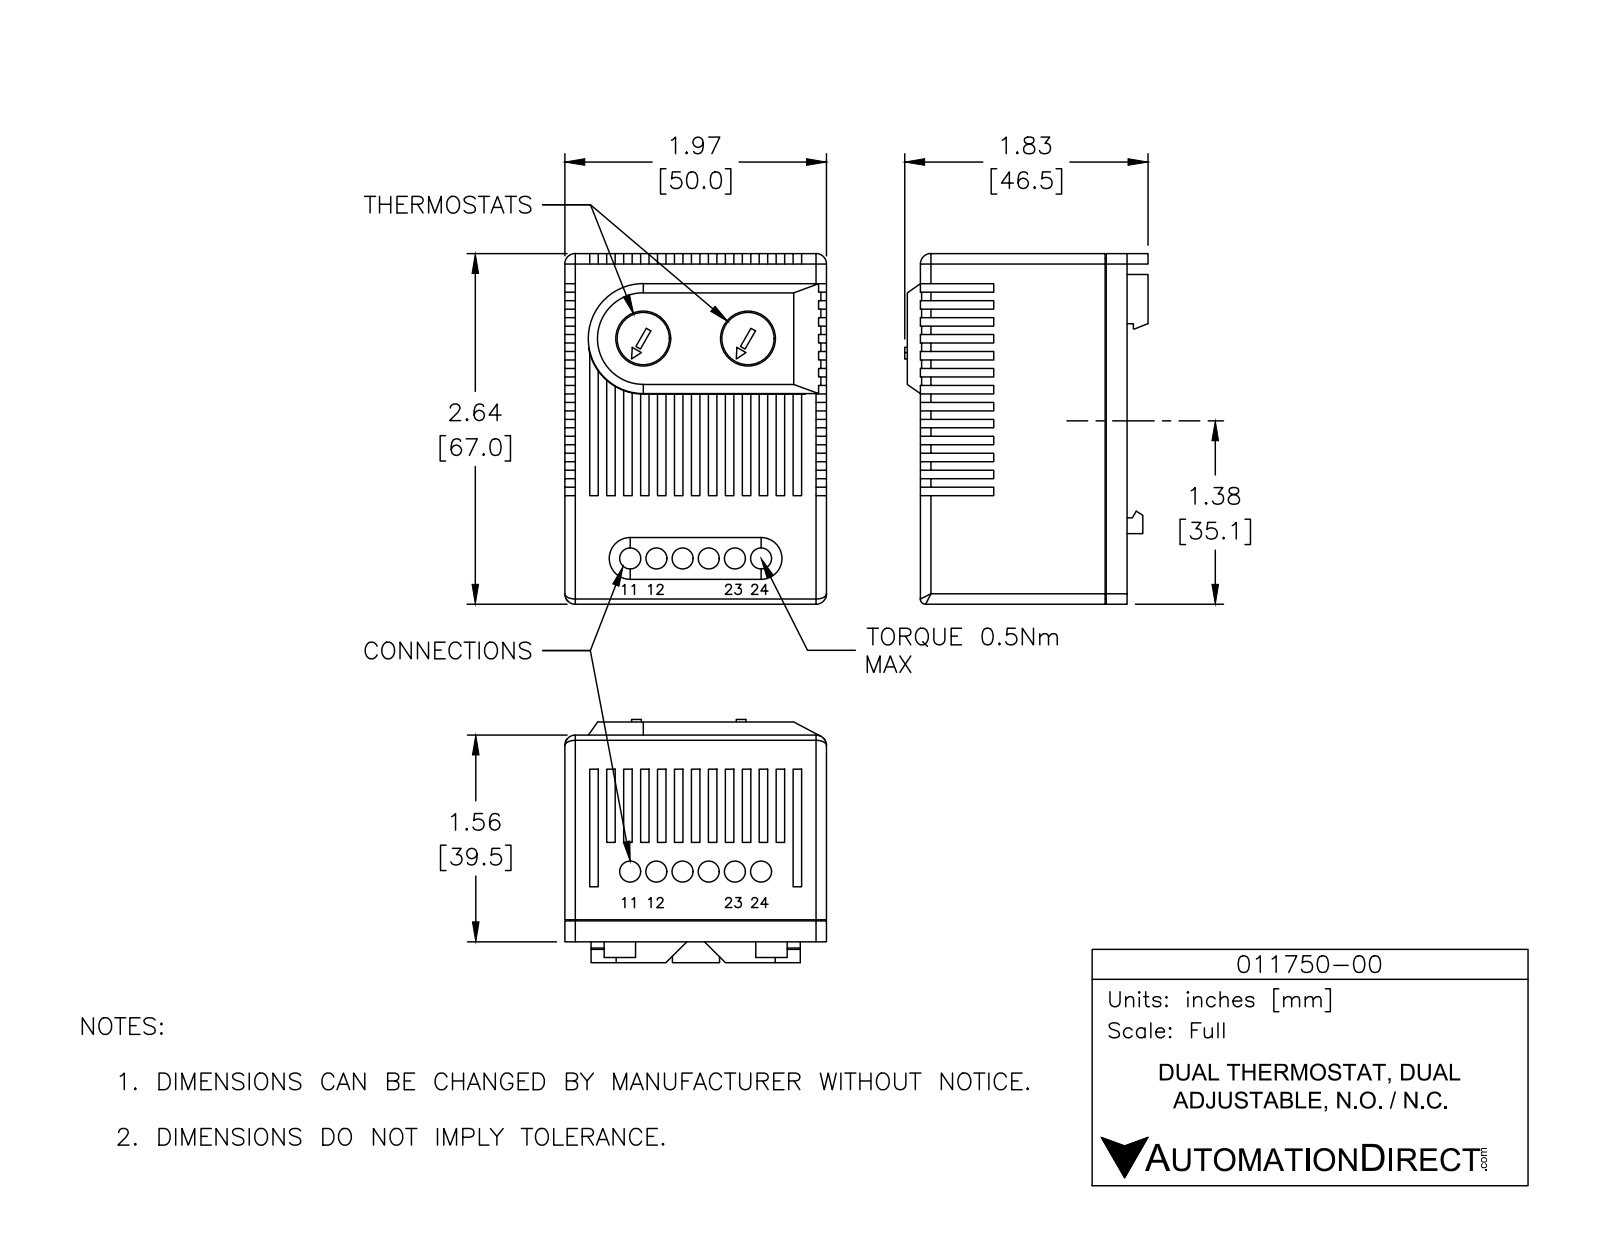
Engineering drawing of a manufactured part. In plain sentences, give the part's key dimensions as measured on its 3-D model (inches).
The part is named "011750-00". Its 3-D file was written by "SolidWorks 2017 (AUTOMOTIVE_DESIGN)". It is 2 solids with 656 faces: 507 planar, 93 cylindrical and 56 other. Overall it measures 2.656 by 1.969 by 1.831 inches. Its volume is 7.939 cubic inches and its surface area 35.94 square inches. Round holes: 12 of diameter 0.157, 2 of diameter 0.413. Round bosses or shafts: 2 of diameter 0.394. Partial cylindrical surfaces (rounded edges, fillets, slot ends): 7 of radius 0.079, 5 of radius 0.039, 1 of radius 0.054, 1 of radius 0.06, 1 of radius 0.157, 1 of radius 0.413, 1 of radius 0.417. The main face-to-face distances are 1.969, 0.079, 0.128, 1.555, 2.638, 0.064, 0.255, 0.383, 0.191, 0.319. The hole center spacings are 0.197, 0.394, 0.591, 0.787, 1.656, 0.984, 1.68, 1.725.
